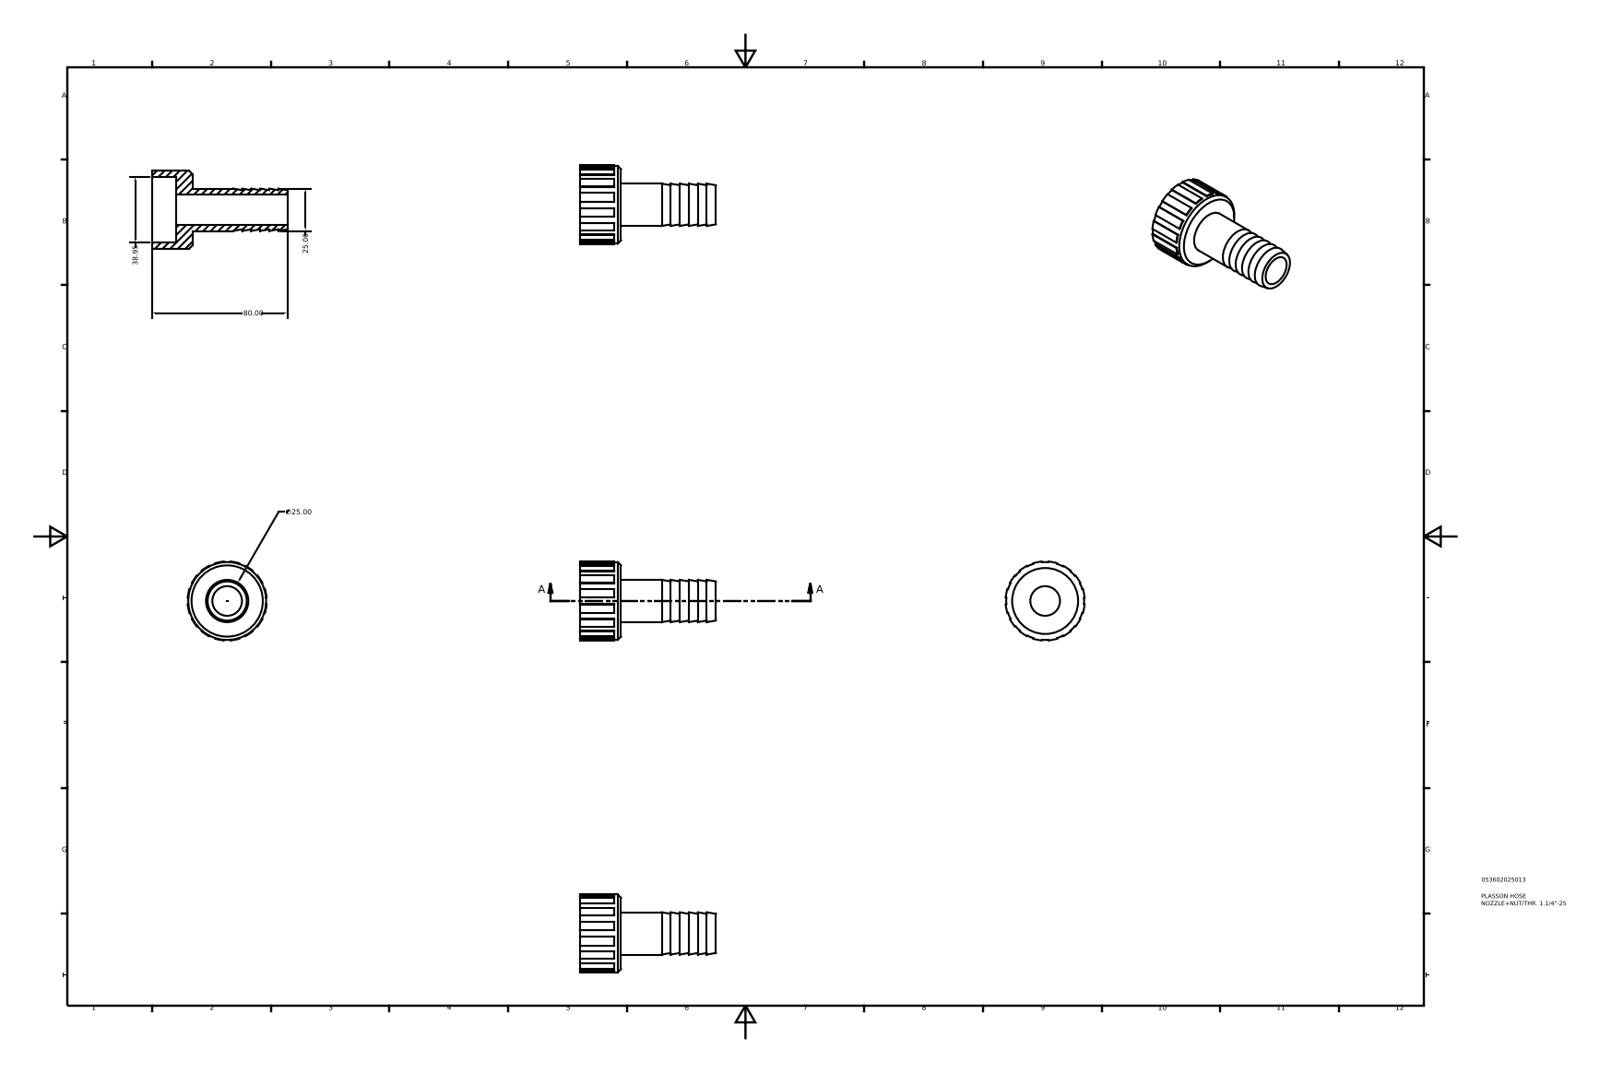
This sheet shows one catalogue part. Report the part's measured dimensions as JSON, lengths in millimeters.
{"part_name": "053602025013", "step_written_by": "Autodesk Inventor 2015 (AUTOMOTIVE_DESIGN)", "units": "millimeters", "bodies": {"solids": 1, "faces": 84, "planar": 57, "cylindrical": 20, "other": 7}, "overall_size": [80, 46.58, 46.58], "volume_mm3": 33607, "surface_area_mm2": 16470, "round_holes": [[17.5, 1], [38.95, 1]], "round_bosses_or_shafts": [[45.96, 1], [25, 1]], "partial_cylinders_radius": [[23.37, 1]], "face_to_face_distances": [9.6, 14.4, 24, 10.67, 16, 5.33, 80, 65.6, 56, 5.34]}
